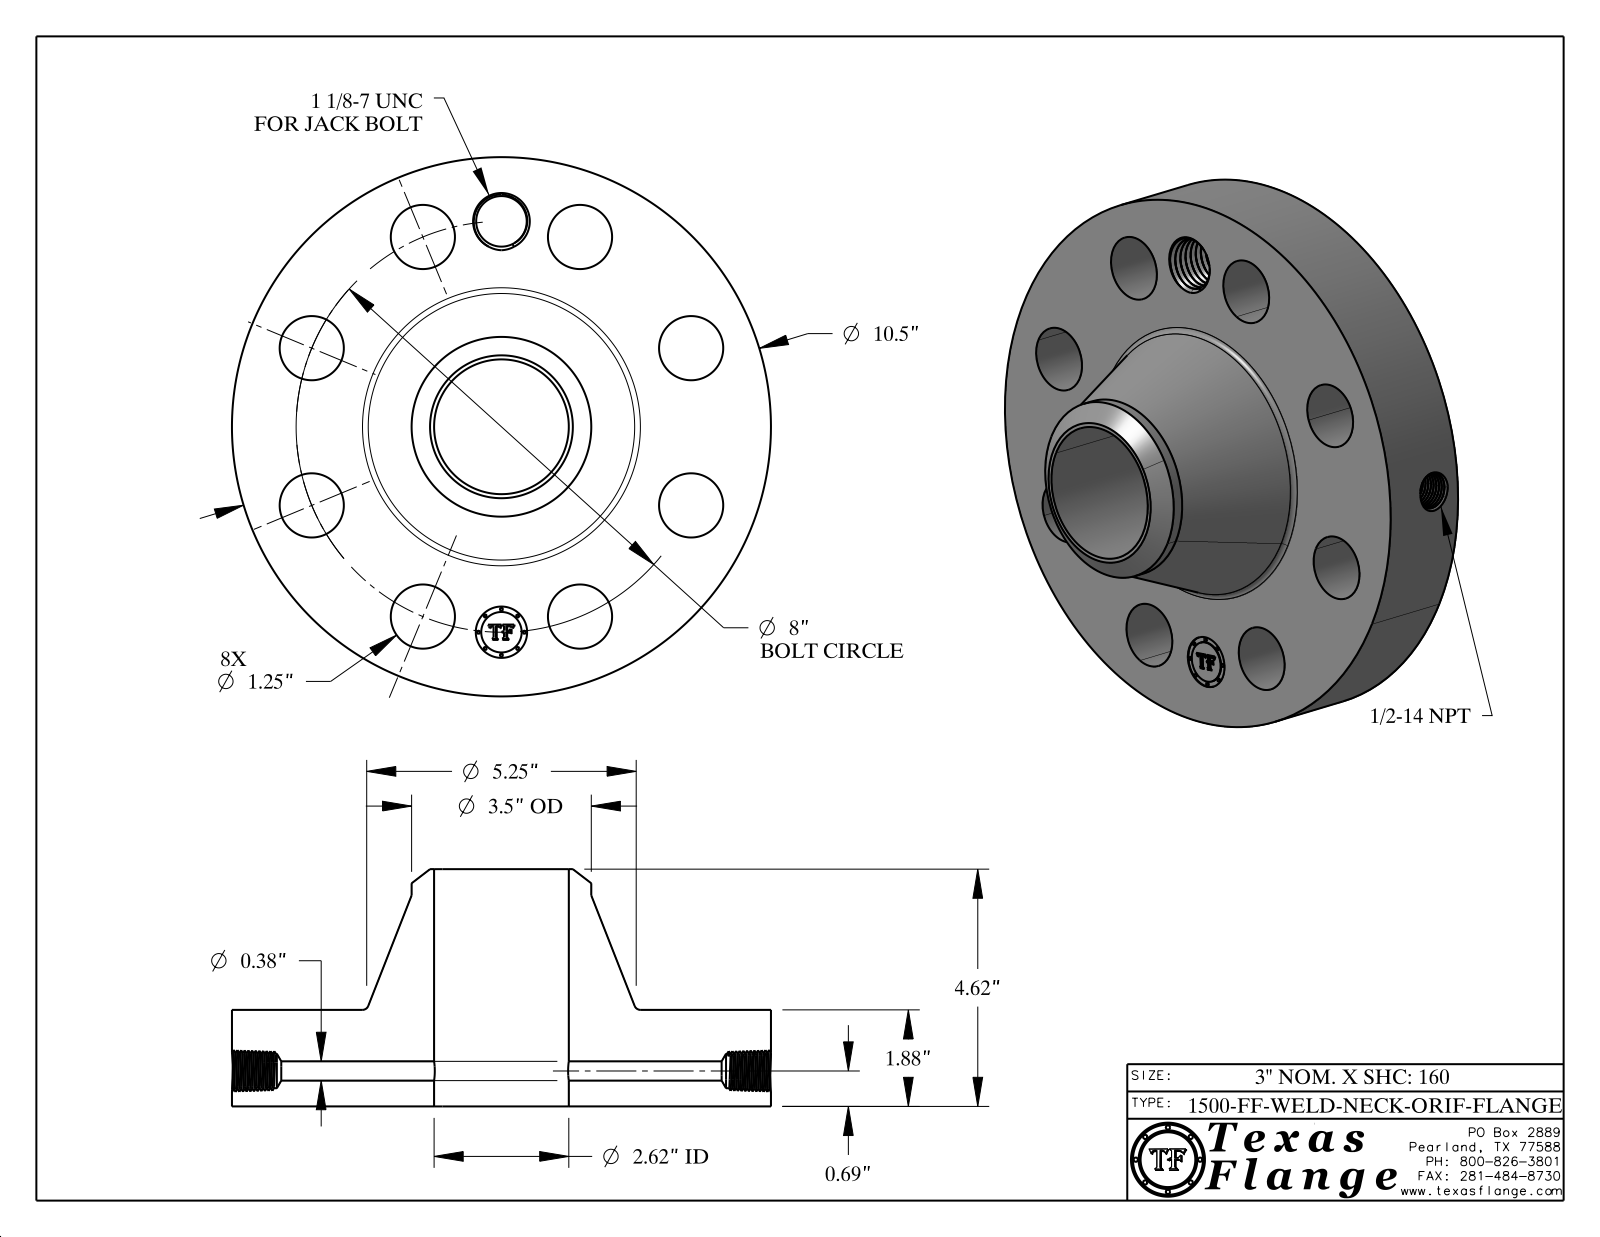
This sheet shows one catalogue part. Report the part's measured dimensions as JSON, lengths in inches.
{"part_name": "1500-FF-WELD-NECK", "step_written_by": "CATIA V5 STEP AP214 (AUTOMOTIVE_DESIGN)", "units": "inches", "bodies": {"solids": 1, "faces": 757, "planar": 368, "cylindrical": 88, "other": 301}, "overall_size": [10.5, 10.5, 4.62], "volume_in3": 154.6, "surface_area_in2": 346.7, "round_holes": [[1.25, 8], [0.375, 1], [0.672, 1], [0.984, 1], [1, 1], [2.624, 1]], "round_bosses_or_shafts": [[0.061, 8], [10.5, 1], [3.5, 1], [0.788, 1]], "face_to_face_distances": [1.88, 4.62, 2.74, 1.865, 0.015, 2.755, 0.298, 0.293, 0.054, 0.248], "hole_center_spacings": [4, 5.657, 7.391, 1.561, 3.061, 3.062, 4.445, 6.652]}
